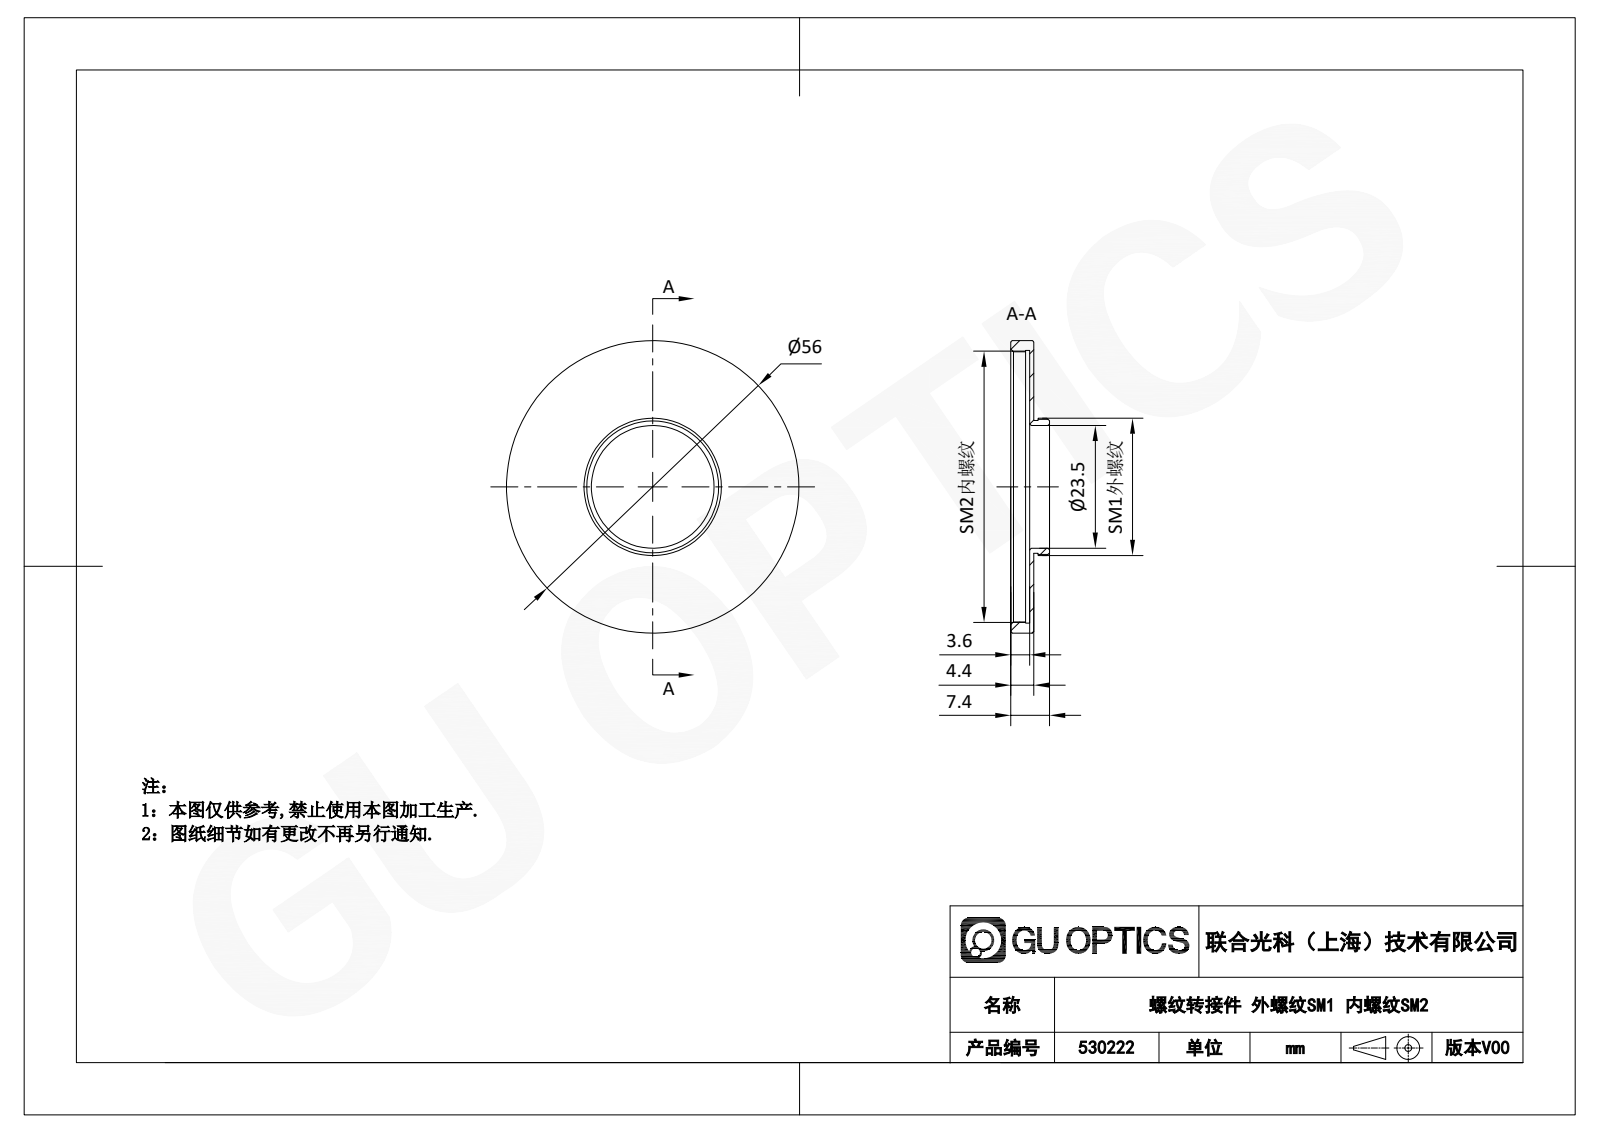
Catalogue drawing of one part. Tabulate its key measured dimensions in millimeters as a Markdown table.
| quantity | value |
| --- | --- |
| part name | 530222 |
| STEP written by | SolidWorks 2020 (CONFIG_CONTROL_DESIGN) |
| units | millimeters |
| bodies | 1 solid, 18 faces (6 planar, 6 cylindrical, 6 other) |
| overall size | 56 × 56 × 7.4 |
| volume | 3 160 mm³ |
| surface area | 5 963 mm² |
| round holes (diameter × count) | 23.5 × 1, 51.69 × 1, 52.2 × 1 |
| round bosses / shafts (diameter × count) | 56 × 1, 26.29 × 1, 25.4 × 1 |
| main face-to-face distances | 0.8, 4.4, 3.6, 1.6, 3, 3.8, 7.4, 4.6, 2.8, 2.2 |
